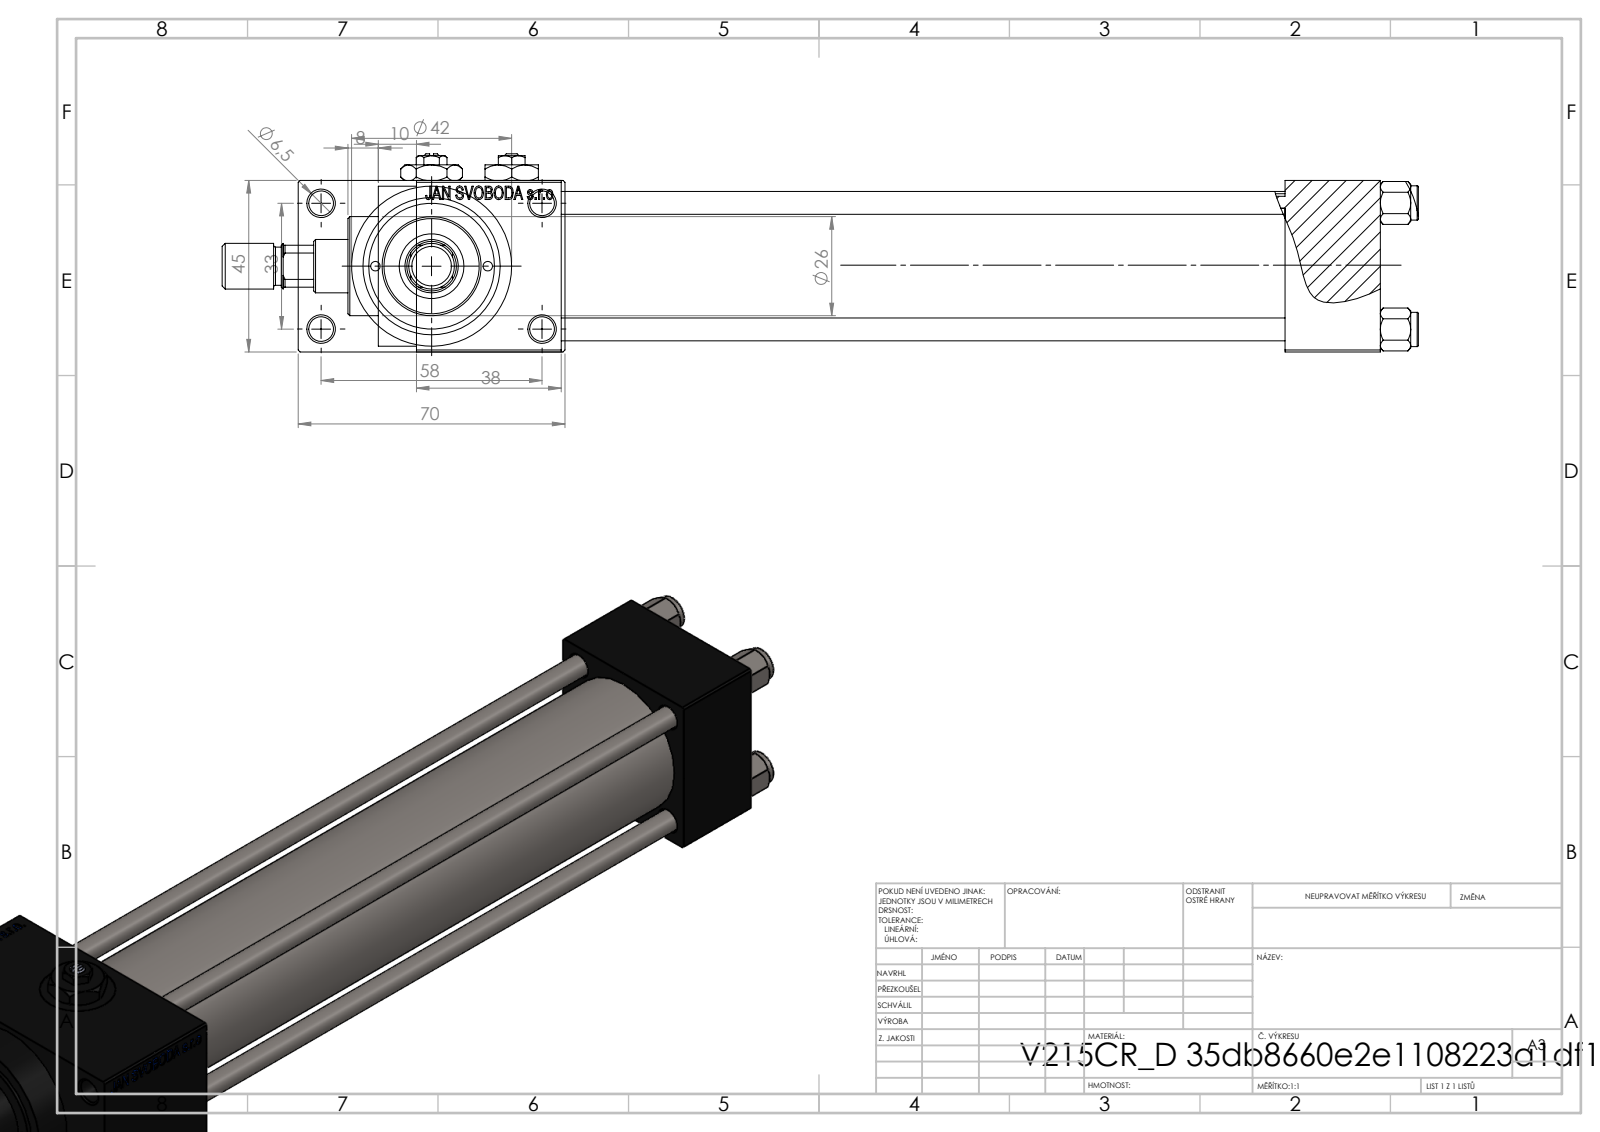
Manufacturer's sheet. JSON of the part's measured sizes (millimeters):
{"part_name": "V215CR_VCP_D; V215CR_D_TYCINKA; V215_VC_A; NUT_M5_D (+3 more)", "step_written_by": "SolidWorks 2019 (CONFIG_CONTROL_DESIGN)", "units": "millimeters", "bodies": {"solids": 13, "faces": 1171, "planar": 525, "cylindrical": 100, "other": 546}, "overall_size": [314, 70, 52], "volume_mm3": 315373, "surface_area_mm2": 124330, "round_holes": [[6.5, 5], [6, 4], [13.16, 3], [20, 3], [2.5, 2], [7, 2], [14, 1], [17, 1], [24, 1], [32, 1], [33, 1]], "round_bosses_or_shafts": [[9, 4], [42, 1], [38, 1], [26, 1], [12, 1], [10, 1]], "partial_cylinders_radius": [[6.5, 1]], "face_to_face_distances": [45, 25, 12.5, 190, 215, 57.5, 228, 38, 253, 70], "hole_center_spacings": [12.4, 16.7, 21.8, 23.48, 33.2, 33.37, 35.35, 35.47]}
